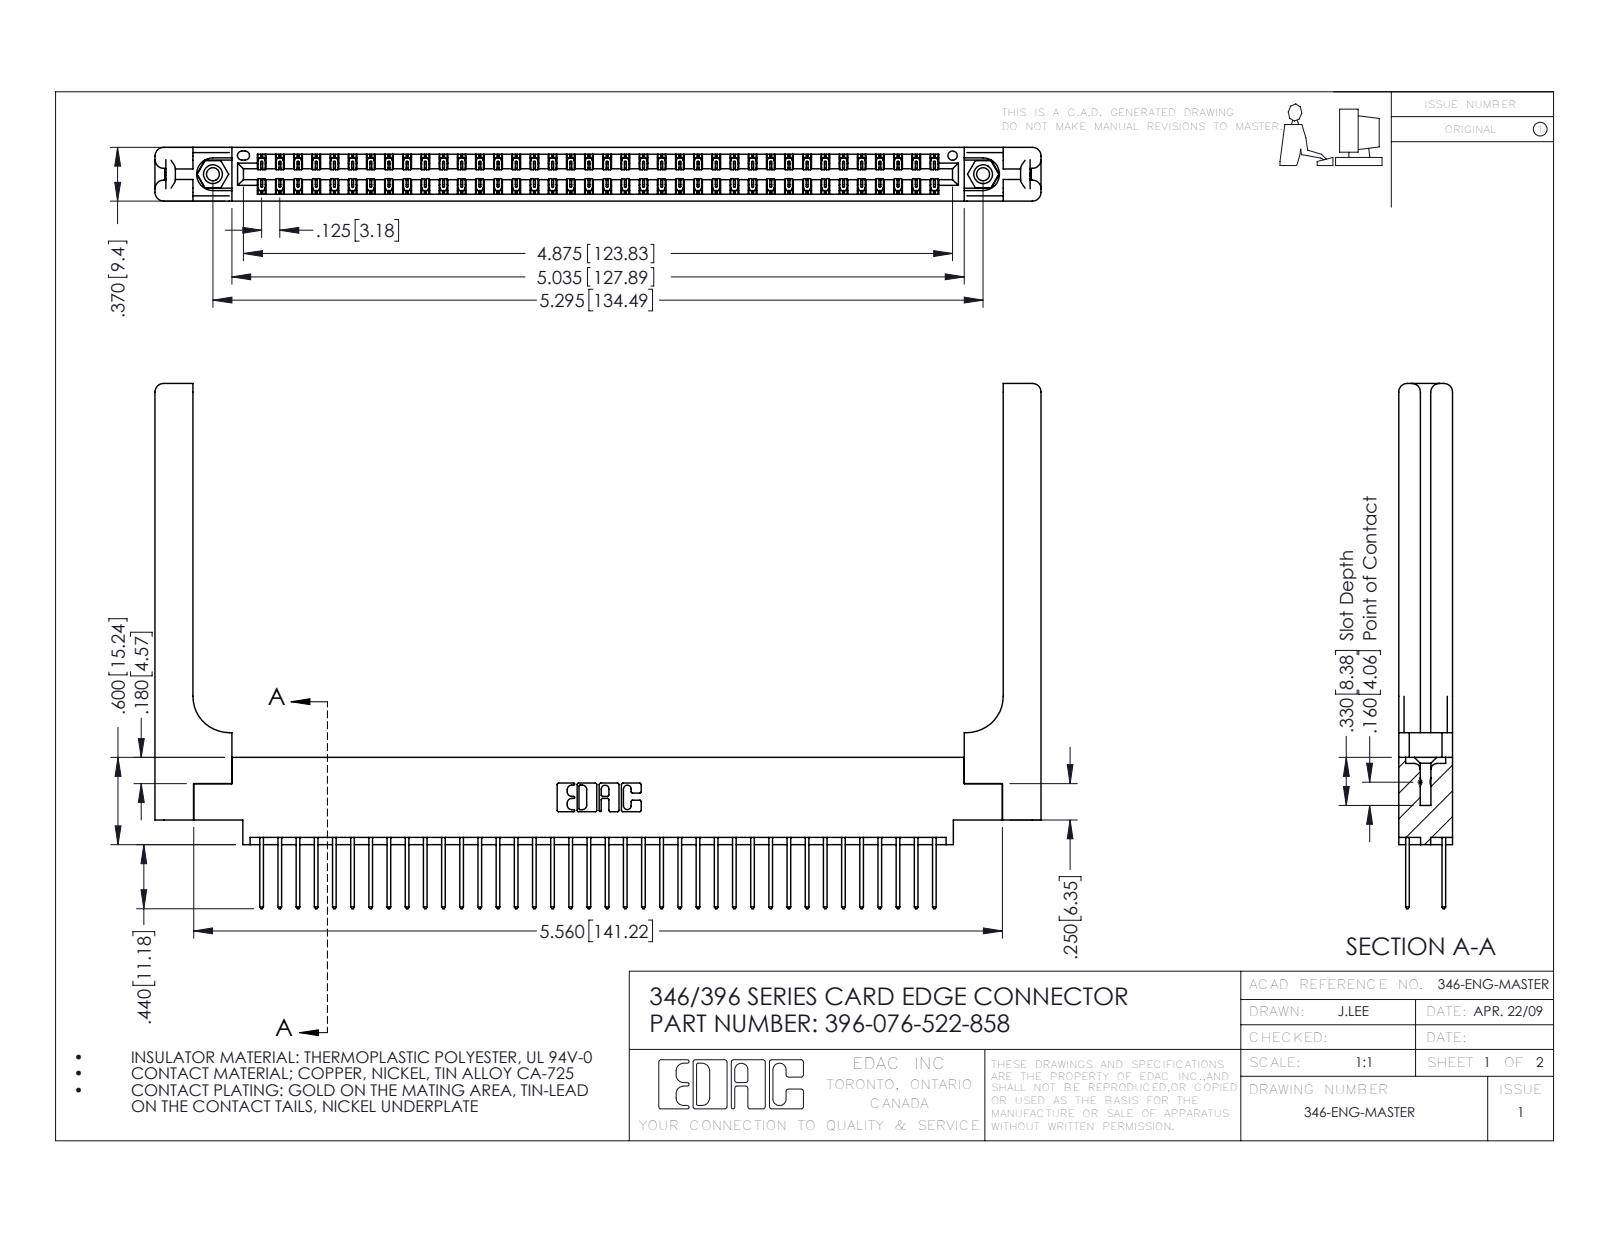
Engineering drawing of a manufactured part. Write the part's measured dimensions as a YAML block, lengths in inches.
part_name: "346 Part_0.170 Offset - 0.156 Dia-TH; 396-076-522-858; 345-292-001_345-293-122; 346-220-058_345-220-058 (+1 more)"
step_written_by: "SolidWorks 2016 (CONFIG_CONTROL_DESIGN)"
units: inches
bodies: {solids: 81, faces: 4334, planar: 2888, cylindrical: 1386, other: 60}
overall_size: [6.091, 3.61, 0.37]
volume: 1.378
surface_area: 41.45
round_holes:
  - {diameter: 0.089, count: 2}
  - {diameter: 0.125, count: 2}
  - {diameter: 0.156, count: 2}
  - {diameter: 0.064, count: 1}
round_bosses_or_shafts:
  - {diameter: 0.155, count: 2}
partial_cylinders:
  - {radius: 0.006, count: 114}
  - {radius: 0.01, count: 76}
  - {radius: 0.01, count: 22}
  - {radius: 0.06, count: 16}
  - {radius: 0.007, count: 6}
  - {radius: 0.031, count: 6}
  - {radius: 0.026, count: 3}
  - {radius: 0.014, count: 2}
face_to_face_distances: [0.048, 0.322, 0.37, 0.072, 0.25, 0.025, 0.298, 0.148, 0.15, 0.275]
hole_center_spacings: [0.246, 5.086, 5.295]
